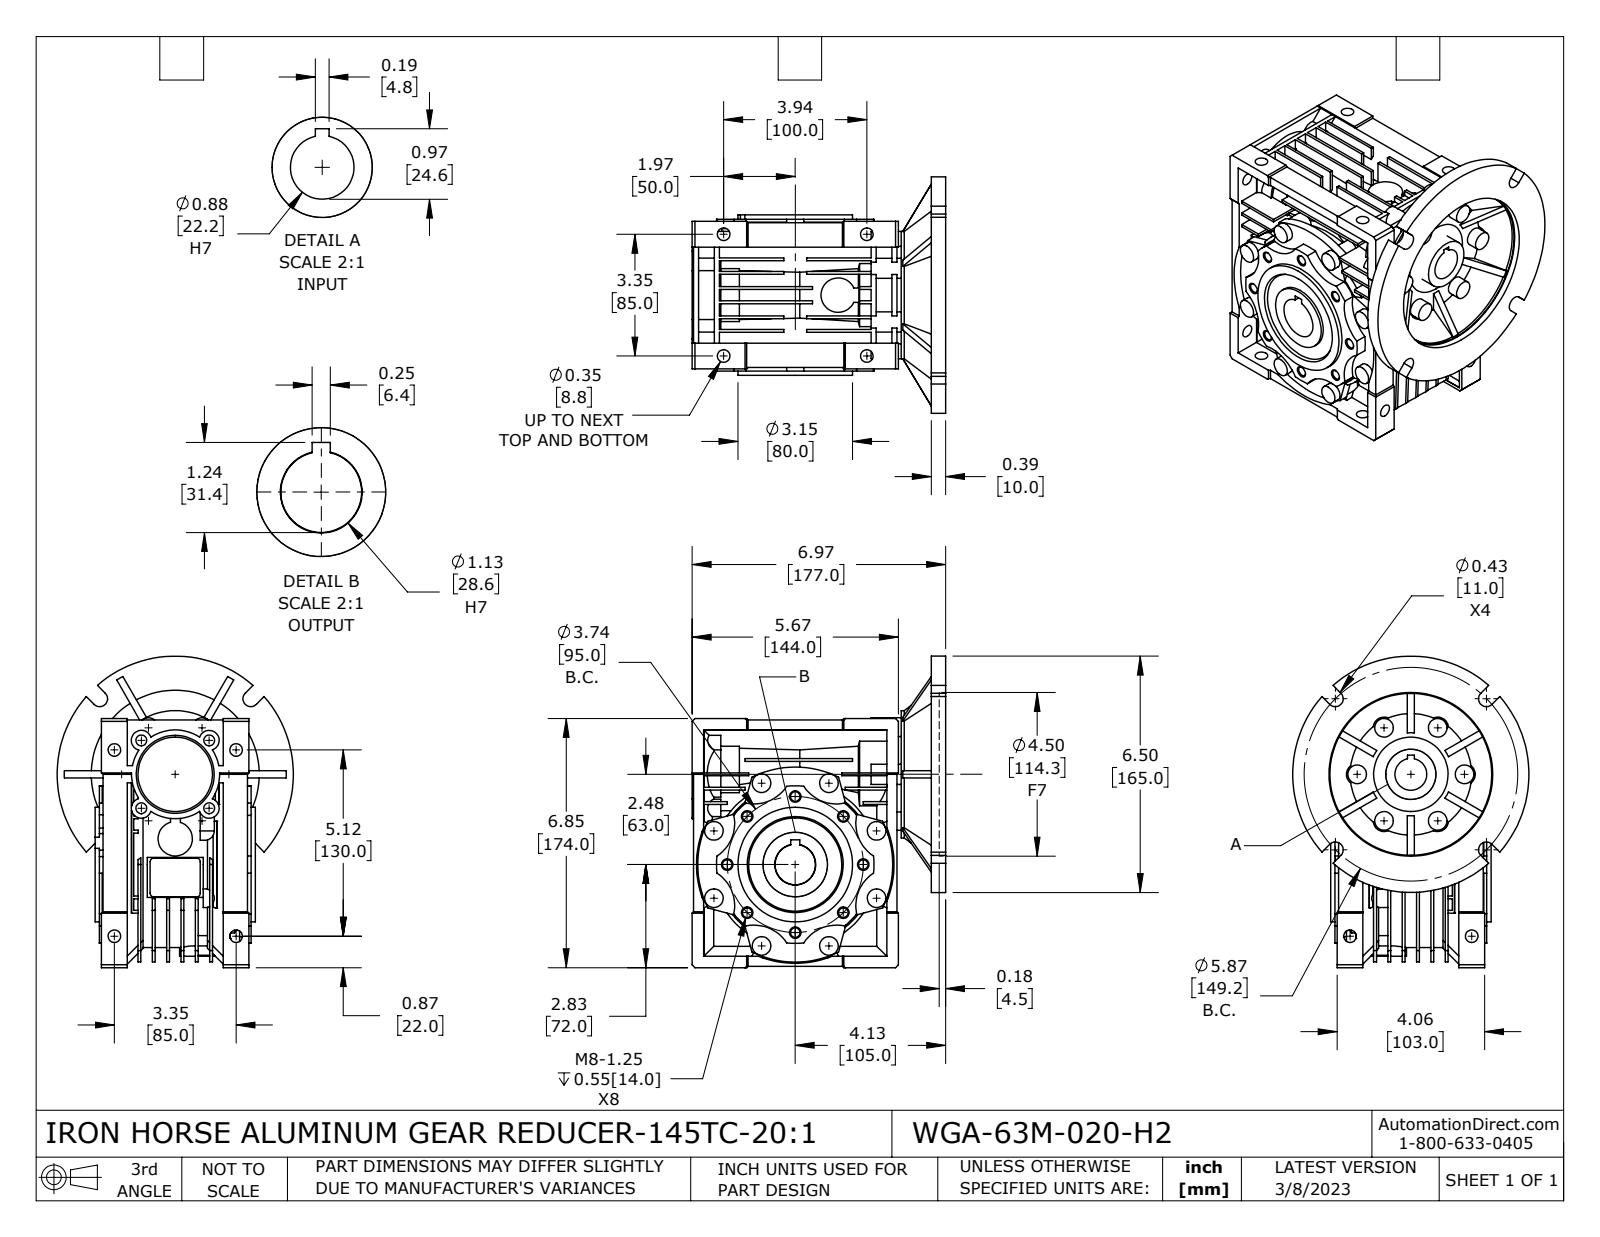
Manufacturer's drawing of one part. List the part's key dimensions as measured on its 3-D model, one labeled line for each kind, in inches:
Part name (STEP PRODUCT): WGA-63M-020-H2
STEP written by: SolidWorks 2021 (CONFIG_CONTROL_DESIGN)
Units: inches
Bodies: 4 solids, 1230 faces (759 planar, 331 cylindrical, 140 other)
Overall size (bounding box): 8.563 × 6.969 × 6.496
Volume: 116.3 in³ · Surface area: 570.4 in²
Round holes (diameter × count): ⌀0.262 ×8, ⌀0.262 ×8, ⌀0.346 ×8, ⌀0.298 ×4, ⌀0.875 ×1, ⌀0.906 ×1, ⌀1.125 ×1, ⌀1.339 ×1, ⌀1.457 ×1, ⌀1.772 ×1, ⌀2.047 ×1, ⌀4.449 ×1
Round bosses / shafts (diameter × count): ⌀0.512 ×14, ⌀0.945 ×3, ⌀6.496 ×1, ⌀4.331 ×1, ⌀3.504 ×1, ⌀3.15 ×1, ⌀2.717 ×1, ⌀2.441 ×1
Partial cylindrical surfaces — rounded edges, fillets, slot ends (radius × count): R0.276 ×10, R1.063 ×8, R0.295 ×6, R0.098 ×4, R0.217 ×4, R0.329 ×1, R1.161 ×1, R1.201 ×1
Main face-to-face distances: 0.394, 0.315, 0.787, 0.079, 1.181, 0.276, 0.472, 0.709, 1.575, 1.22
Hole centre spacings: 1.431, 1.87, 2.645, 3.456, 1.319, 1.865, 3.346, 0.786
